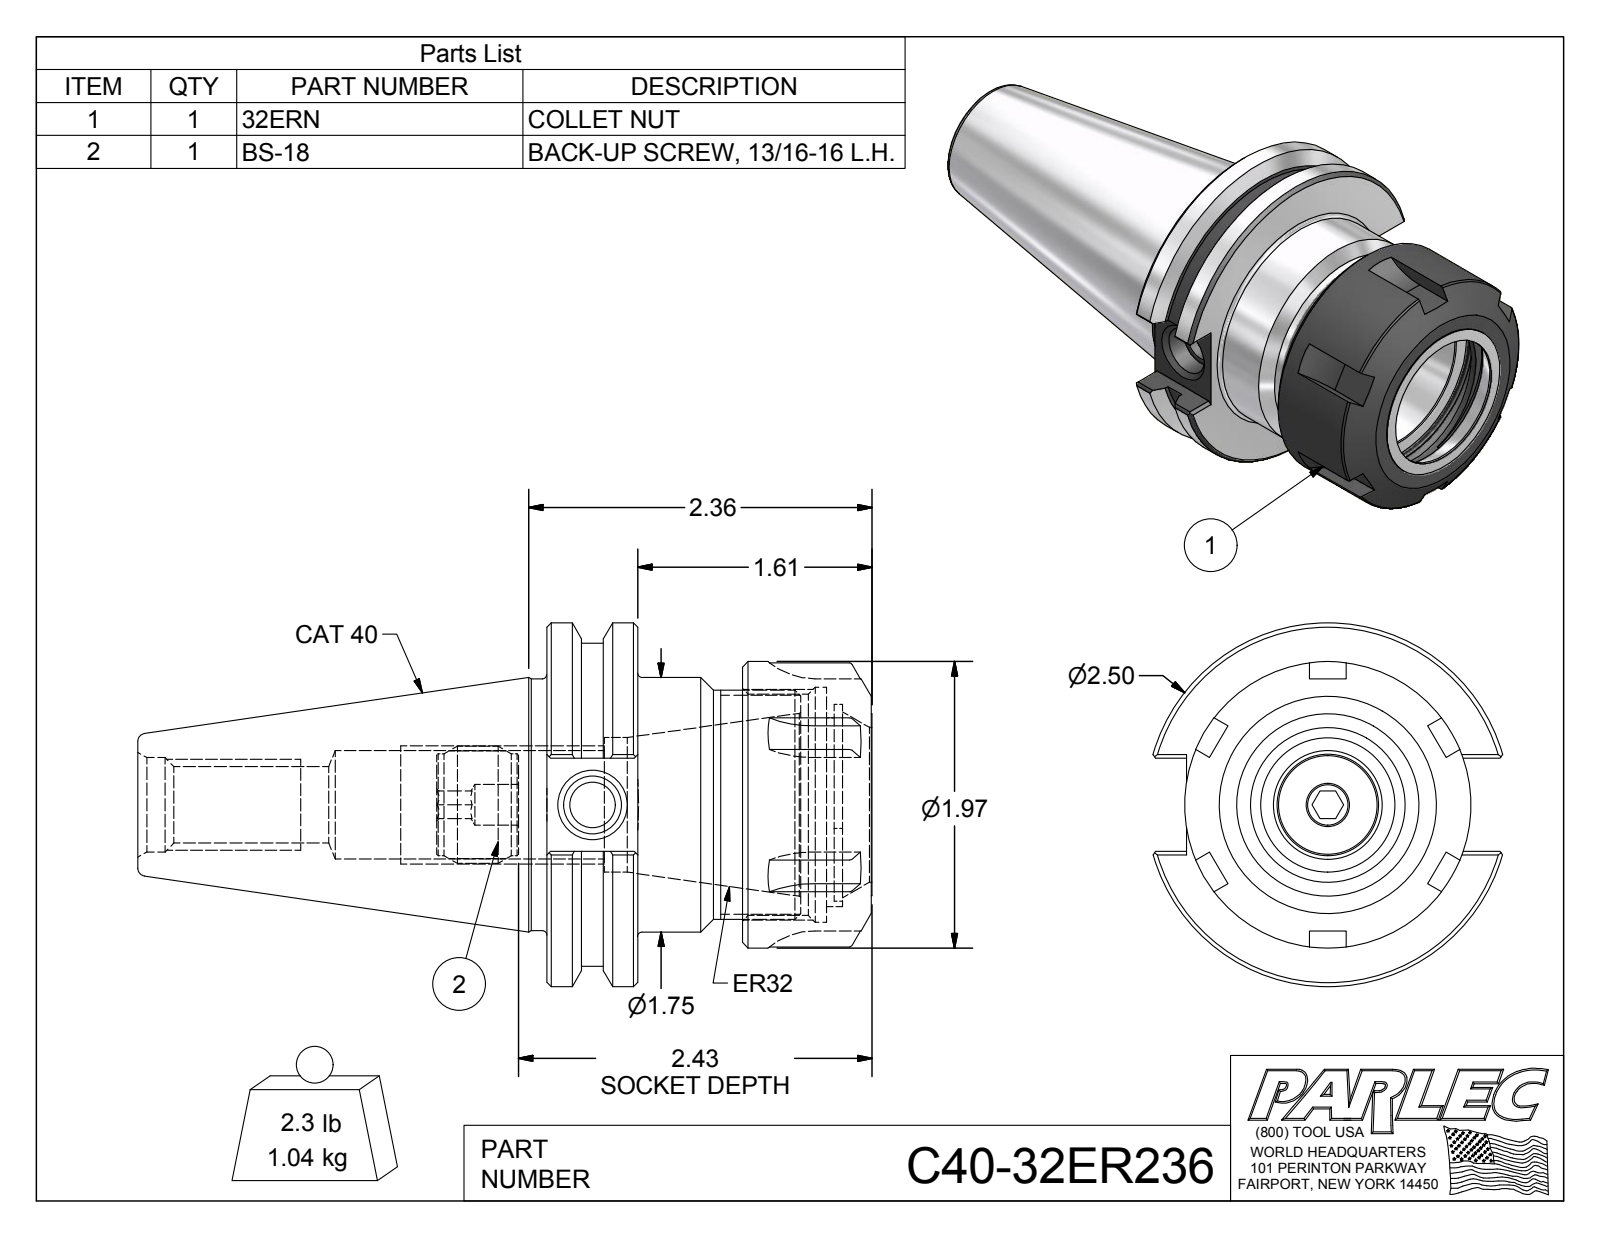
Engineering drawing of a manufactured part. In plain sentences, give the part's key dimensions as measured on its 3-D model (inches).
The part is named "C40-32ER236; C40-32ER236-1; 32ERN; BS-18". Its 3-D file was written by "Autodesk Inventor 2012 (AUTOMOTIVE_DESIGN)". It is 3 solids with 136 faces: 64 planar, 32 cylindrical and 40 other. Overall it measures 5.048 by 2.5 by 2.403 inches. Its volume is 8.231 cubic inches and its surface area 57.89 square inches. Round holes: 1 of diameter 0.28, 1 of diameter 0.315, 1 of diameter 0.396, 1 of diameter 0.527, 1 of diameter 0.648, 1 of diameter 0.745, 1 of diameter 0.925, 1 of diameter 1.063, 1 of diameter 1.299, 1 of diameter 1.522, 1 of diameter 1.614. Round bosses or shafts: 1 of diameter 2.5, 1 of diameter 2.219, 1 of diameter 1.969, 1 of diameter 1.75, 1 of diameter 1.73, 1 of diameter 1.575, 1 of diameter 1.252, 1 of diameter 0.805. Partial cylindrical surfaces (rounded edges, fillets, slot ends): 6 of radius 0.5, 1 of radius 0.689. The main face-to-face distances are 0.625, 1.344, 0.719, 1.922, 1.298, 0.579, 2.23, 1.605, 0.886, 0.307. The hole center spacings are 0.059.
